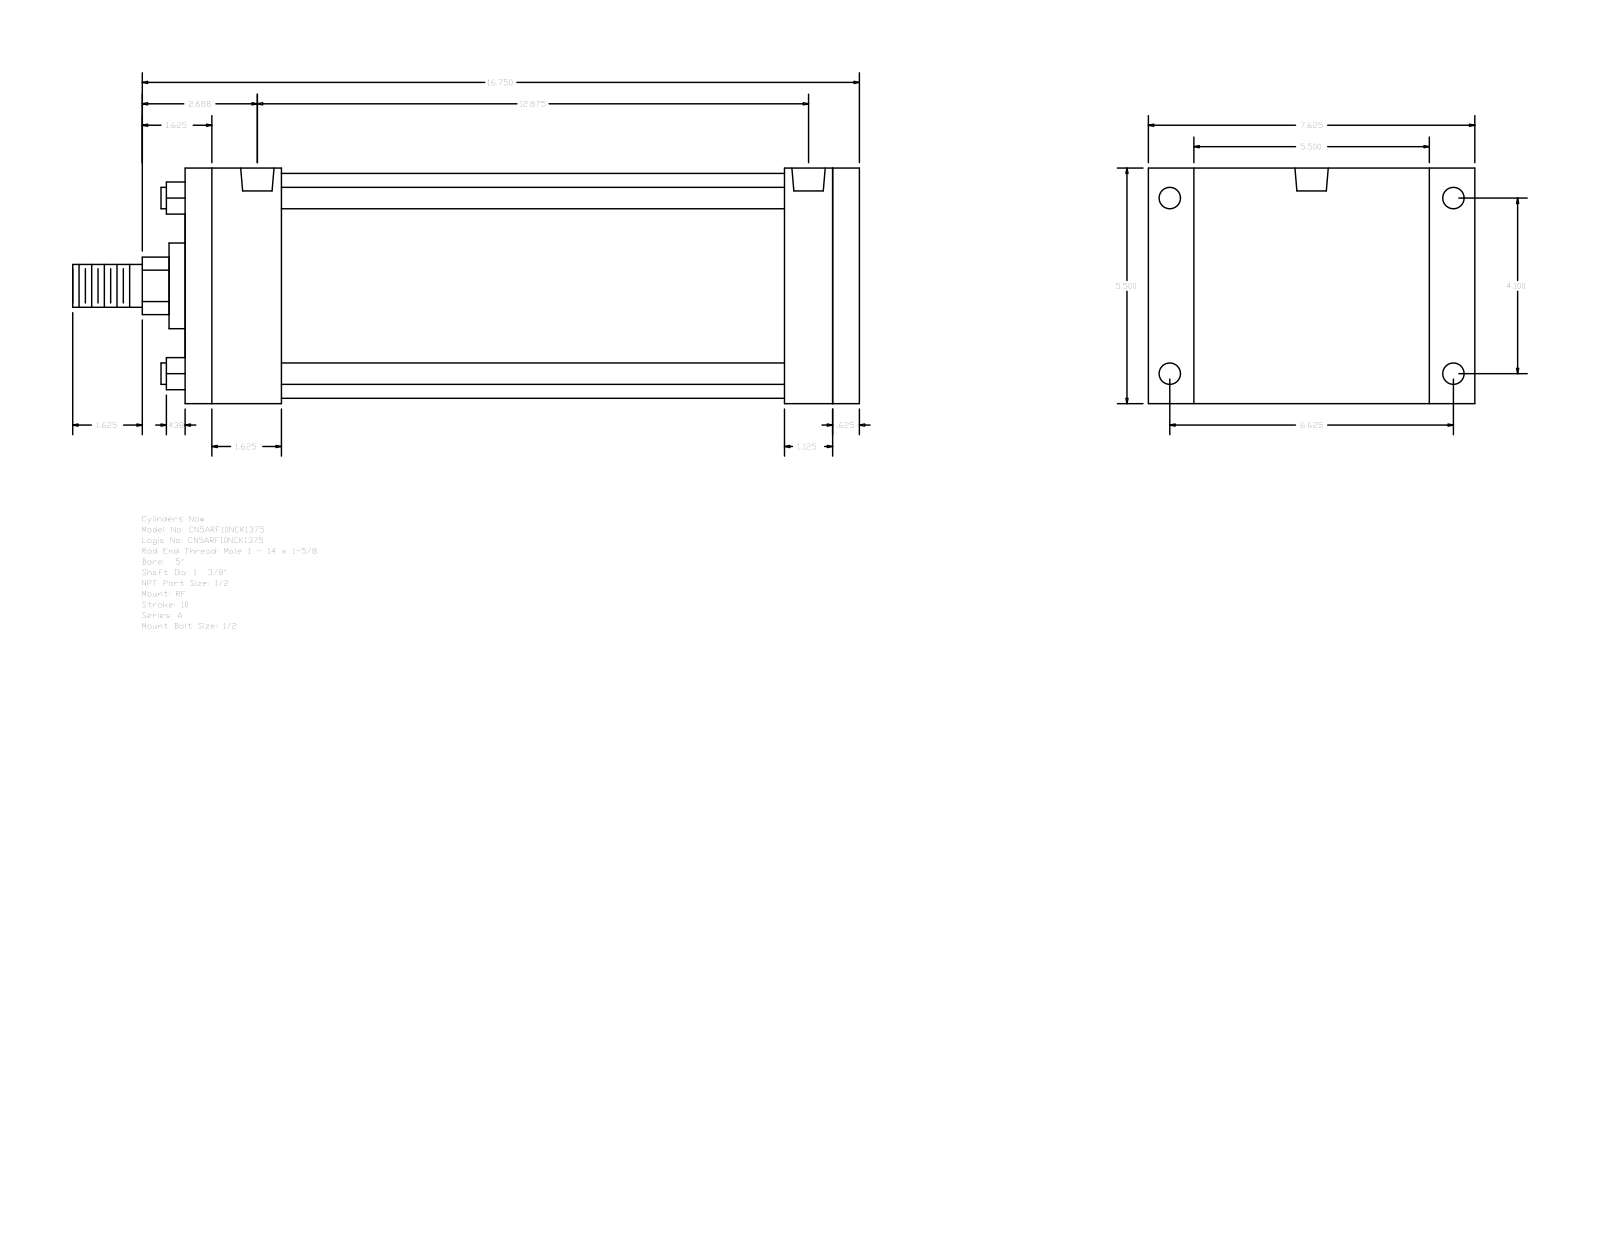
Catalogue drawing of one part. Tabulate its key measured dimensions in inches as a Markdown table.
| quantity | value |
| --- | --- |
| part name | A_RF__0500_1.375 |
| STEP written by | GSSL Pune (CONFIG_CONTROL_DESIGN) |
| units | inches |
| bodies | 0 solids, 92 faces (64 planar, 28 cylindrical, 0 other) |
| overall size | 18.375 × 7.625 × 5.5 |
| round holes (diameter × count) | 0.344 × 4, 0.5 × 4, 0.778 × 2 |
| round bosses / shafts (diameter × count) | 0.5 × 4, 5.25 × 1, 2 × 1, 1.375 × 1, 1 × 1 |
| partial cylindrical surfaces (radius × count) | 0.672 × 1 |
| main face-to-face distances | 5.5, 15.75, 0.625, 15.125, 2.25, 12.875, 13.5, 14, 11.75, 1.125 |
| hole center spacings | 0.094, 4.1, 6.625, 7.791, 12.687, 12.781, 12.875 |
